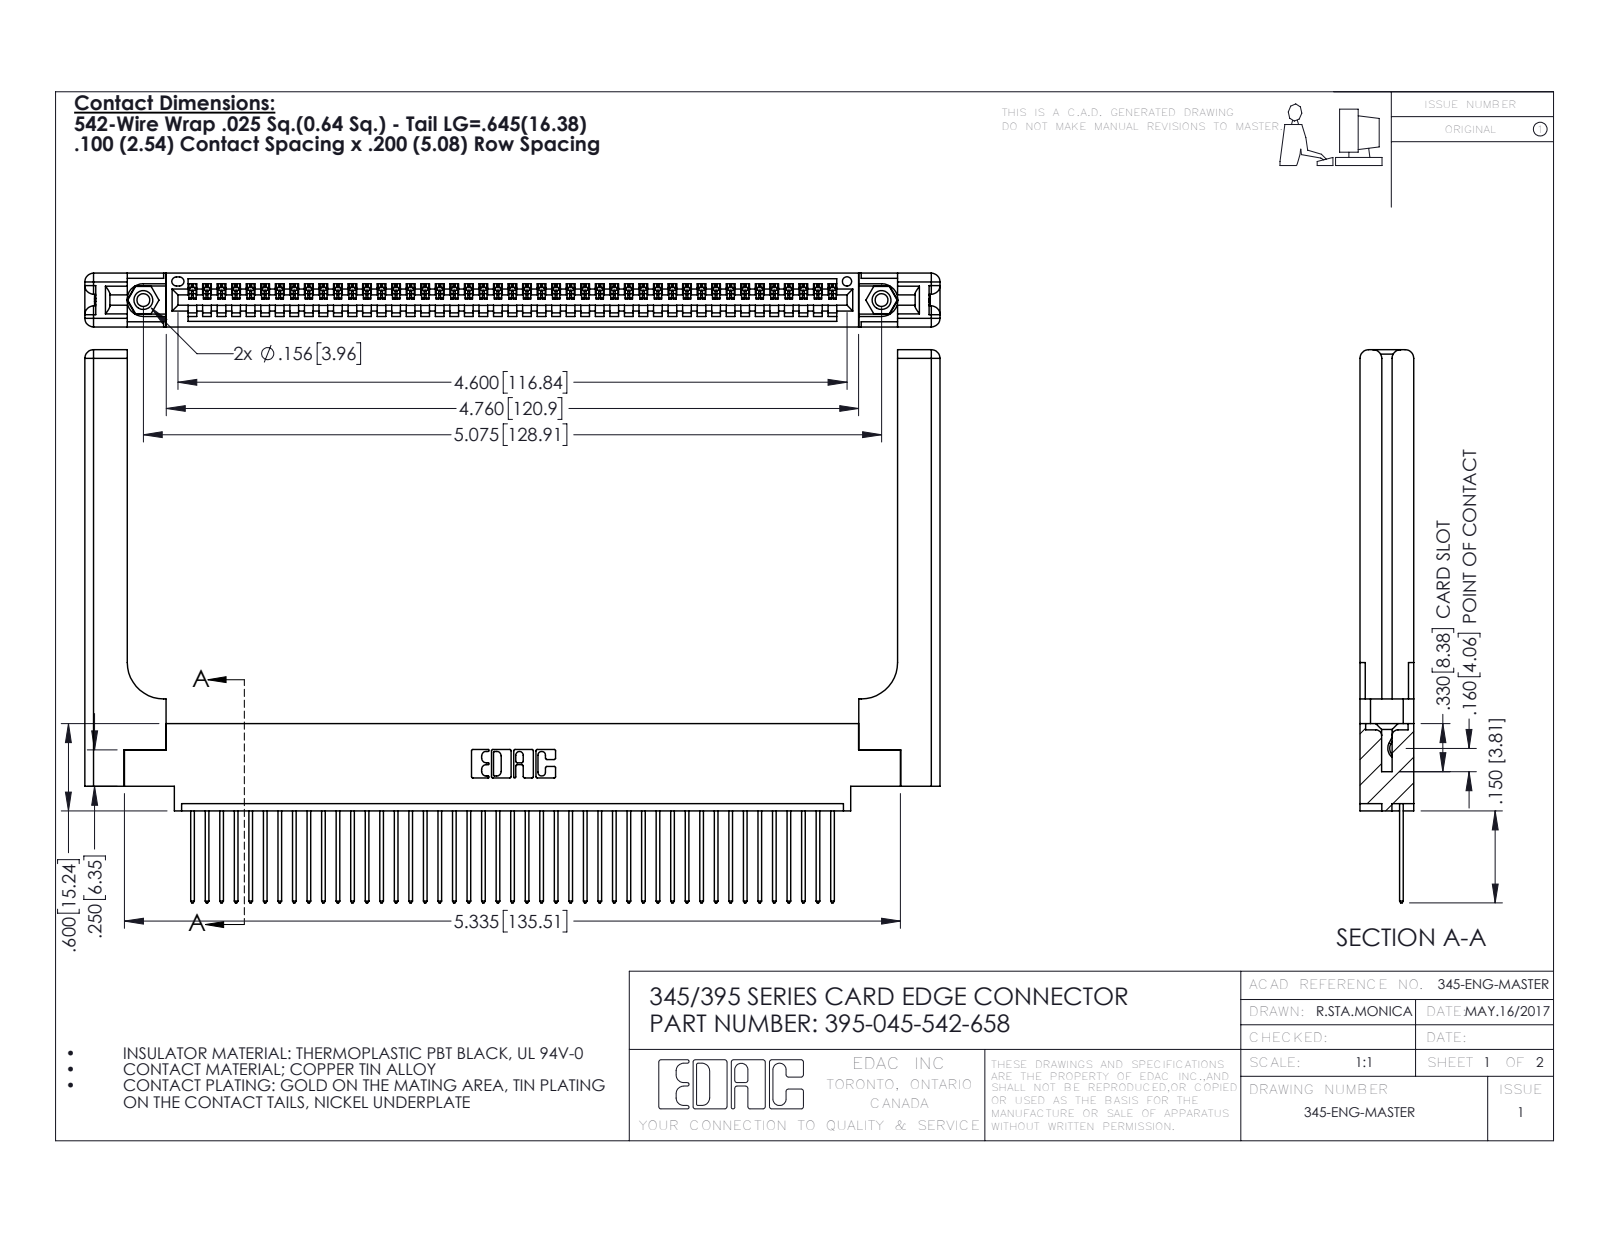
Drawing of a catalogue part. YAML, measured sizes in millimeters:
part_name: "345-292-001_345-293-142; 395-045-542-658; 345-250-001_345-250-001-102; 345-220-058_345-220-058 (+1 more)"
step_written_by: "SolidWorks 2016 (CONFIG_CONTROL_DESIGN)"
units: millimeters
bodies: {solids: 50, faces: 2996, planar: 2032, cylindrical: 904, other: 60}
overall_size: [149.3, 96.6, 9.4]
volume: 22700
surface_area: 24970
round_holes:
  - {diameter: 2.3, count: 2}
  - {diameter: 3.2, count: 2}
  - {diameter: 4, count: 2}
  - {diameter: 1.6, count: 1}
round_bosses_or_shafts:
  - {diameter: 3.9, count: 2}
partial_cylinders:
  - {radius: 0.2, count: 90}
  - {radius: 0.3, count: 90}
  - {radius: 0.3, count: 22}
  - {radius: 1.5, count: 16}
  - {radius: 0.2, count: 6}
  - {radius: 0.8, count: 6}
  - {radius: 0.7, count: 3}
  - {radius: 0.8, count: 2}
face_to_face_distances: [1.8, 9.4, 7.6, 2.5, 6.9, 0.6, 5.1, 5.7, 3.8, 3.8]
hole_center_spacings: [6.9, 122.9, 128.9]
